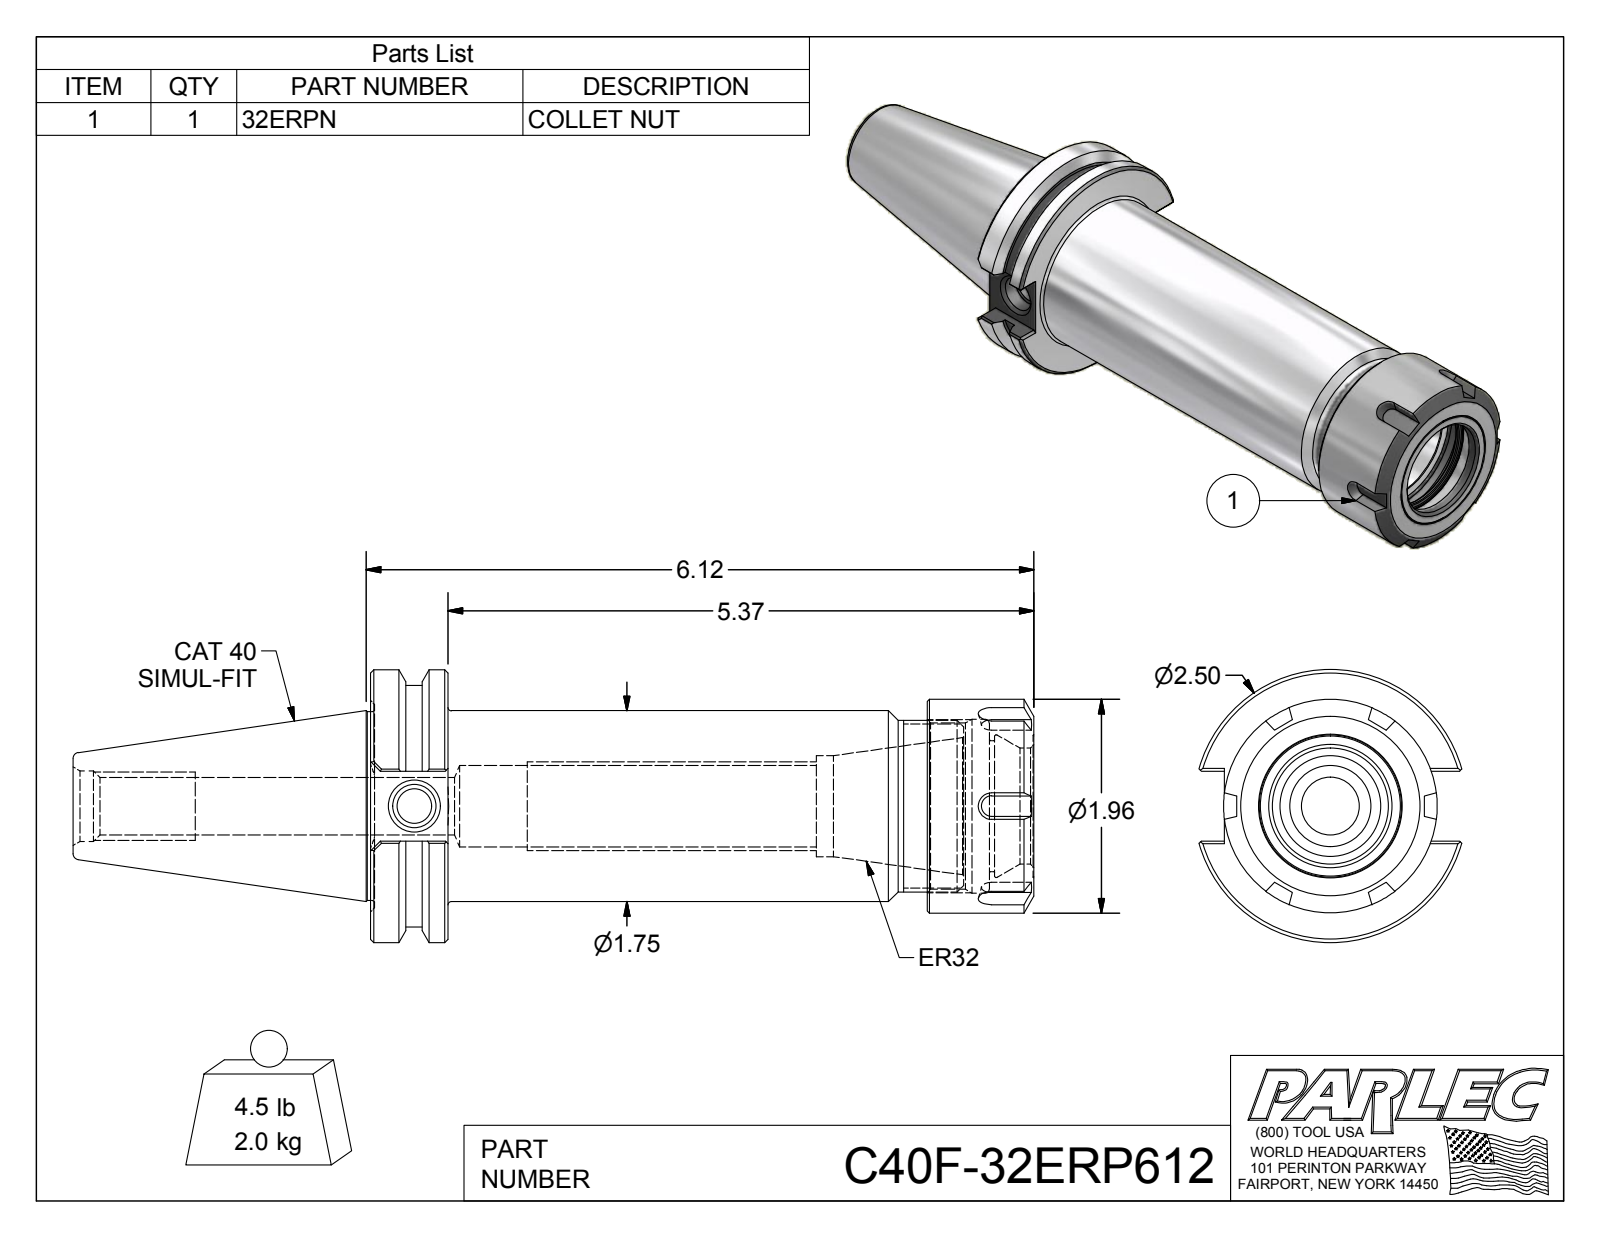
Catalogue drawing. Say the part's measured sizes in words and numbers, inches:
The part is named "C40F-32ERP612; C40F-32ER6-1; 32ERPN". Its 3-D file was written by "Autodesk Inventor 2012 (AUTOMOTIVE_DESIGN)". It is 2 solids with 123 faces: 56 planar, 21 cylindrical and 46 other. Overall it measures 8.808 by 2.5 by 2.406 inches. Its volume is 16 cubic inches and its surface area 83.27 square inches. Round holes: 1 of diameter 0.315, 1 of diameter 0.399, 1 of diameter 0.527, 1 of diameter 0.648, 1 of diameter 0.745, 1 of diameter 0.925, 1 of diameter 1.063, 1 of diameter 1.2, 1 of diameter 1.305, 1 of diameter 1.523, 1 of diameter 1.595. Round bosses or shafts: 1 of diameter 2.5, 1 of diameter 2.215, 1 of diameter 1.958, 1 of diameter 1.75, 1 of diameter 1.73, 1 of diameter 1.575. The main face-to-face distances are 0.711, 6.081, 5.37, 5.103, 4.392, 0.978, 5.674, 4.963, 0.571, 0.407.
